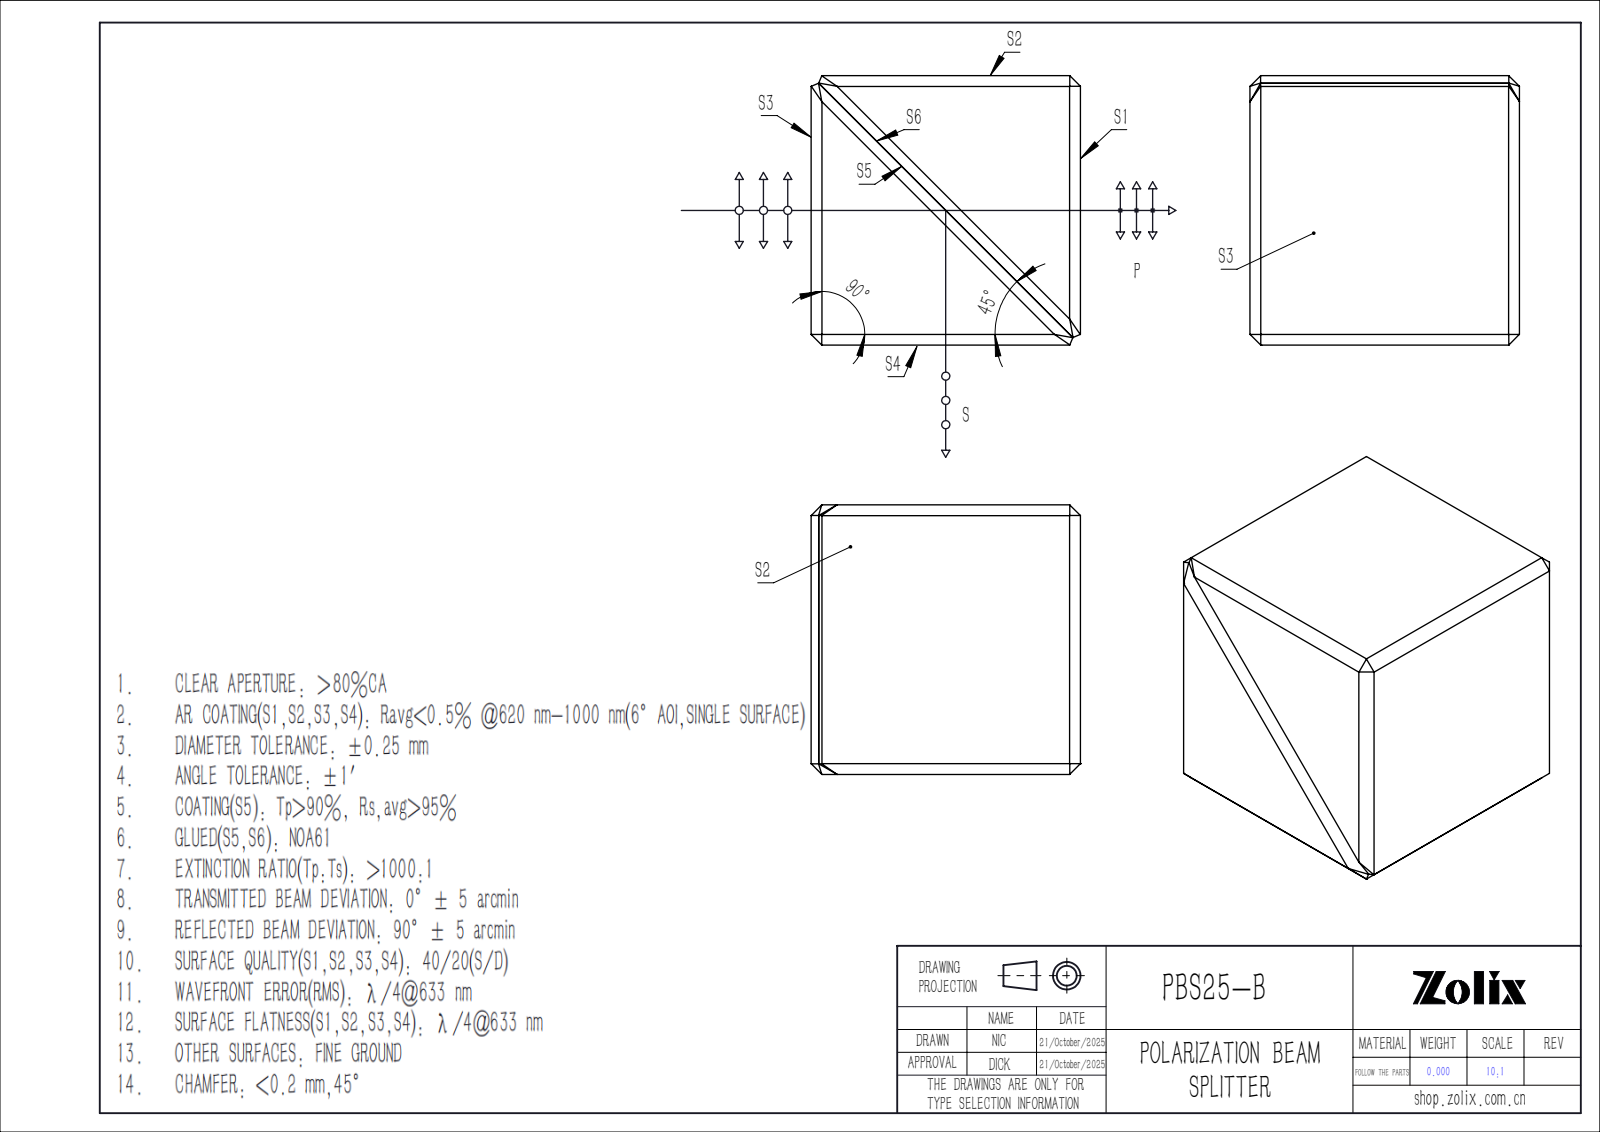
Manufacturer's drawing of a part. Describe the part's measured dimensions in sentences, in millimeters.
The part is named "PBS641-1; PBS641-1-2; PBS641-1-1". Its 3-D file was written by "SolidWorks 2022 (CONFIG_CONTROL_DESIGN)". It is 2 solids with 43 faces: 41 planar, 2 cylindrical and 0 other. Overall it measures 25.4 by 25.4 by 25.4 millimeters. Its volume is 16 378 cubic millimeters and its surface area 5 624 square millimeters. Round holes: 1 of diameter 0.2. The main face-to-face distances are 25.4, 35.63, 17.67, 35.64, 32.83, 17.81, 17.82, 43.51, 38.13, 38.14.
